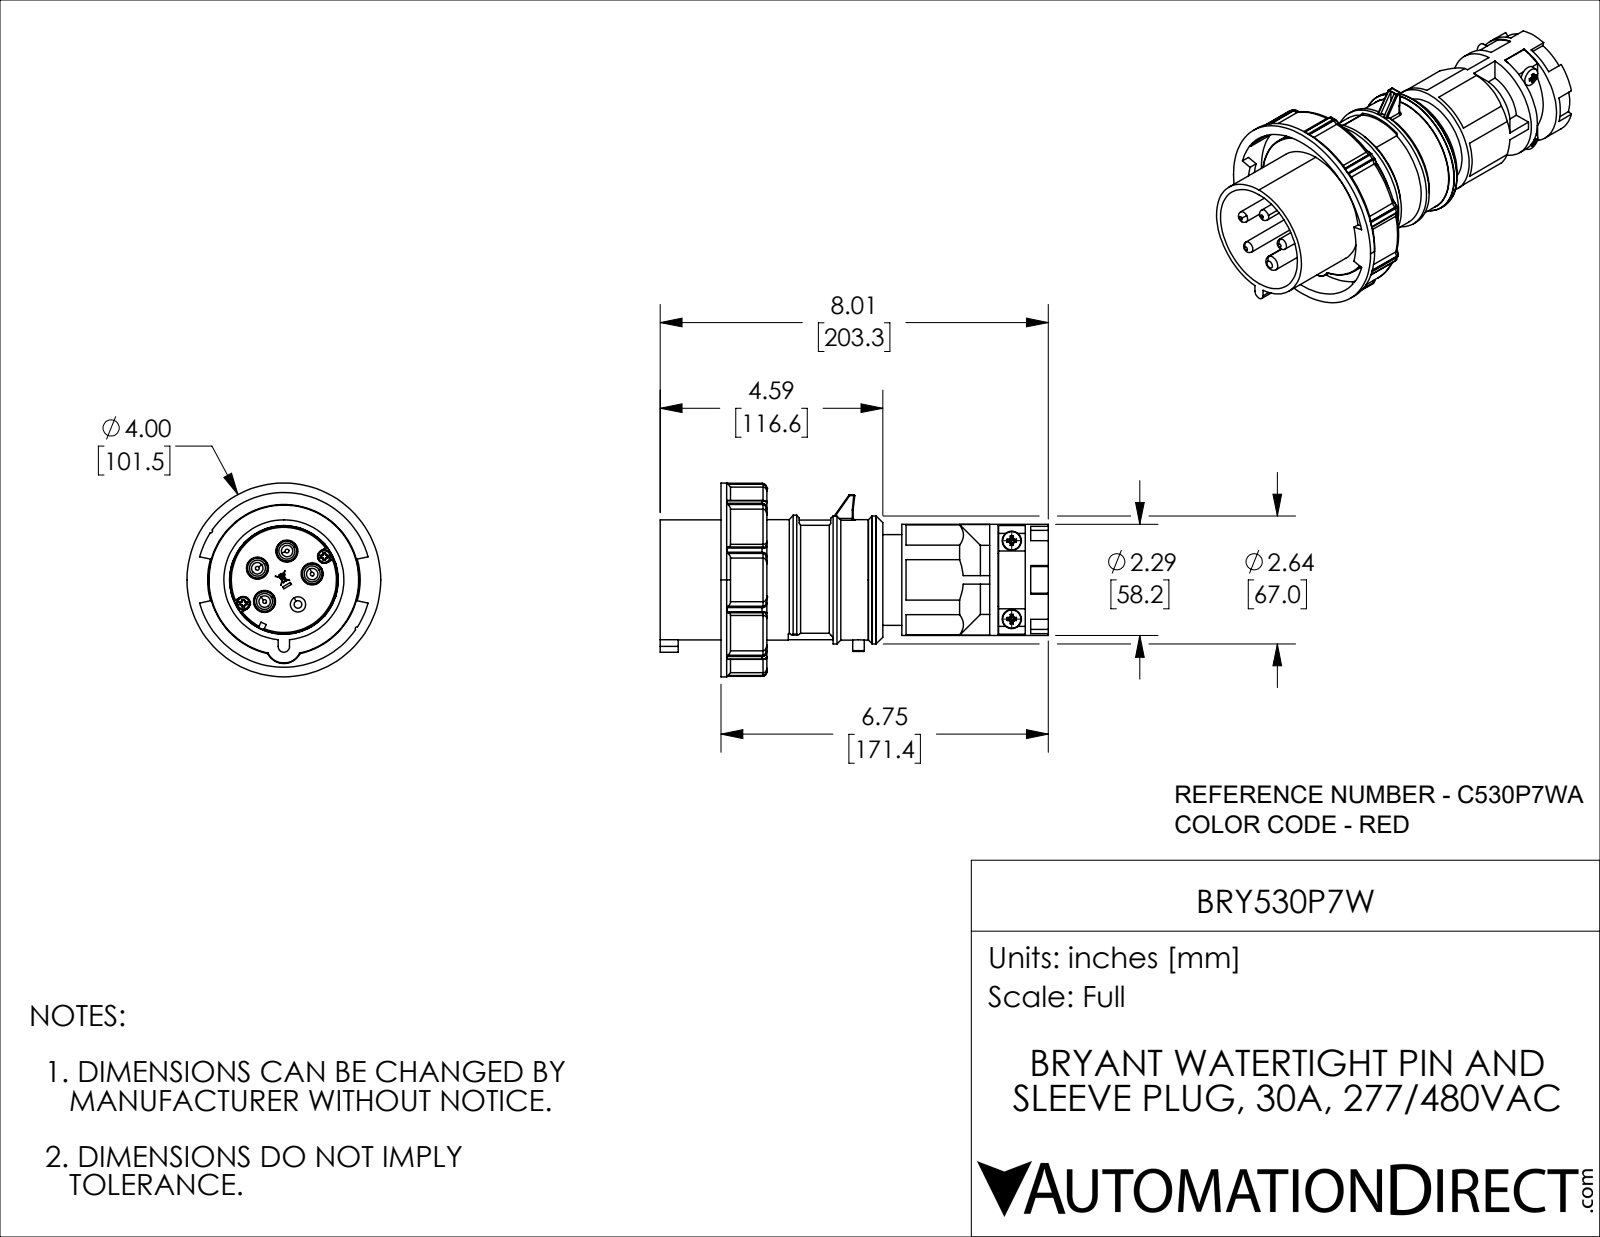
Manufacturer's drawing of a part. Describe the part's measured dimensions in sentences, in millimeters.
The part is named "BRY530P7W". Its 3-D file was written by "SolidWorks 2021 (CONFIG_CONTROL_DESIGN)". It is 6 solids with 861 faces: 337 planar, 266 cylindrical and 258 other. Overall it measures 203.33 by 101.5 by 101.5 millimeters. Its volume is 459 019 cubic millimeters and its surface area 104 002 square millimeters. Round holes: 2 of diameter 5, 1 of diameter 0.51, 1 of diameter 3.1, 1 of diameter 29.5, 1 of diameter 49.04, 1 of diameter 91.5. Round bosses or shafts: 5 of diameter 6, 1 of diameter 101.5, 1 of diameter 79, 1 of diameter 67.7, 1 of diameter 67, 1 of diameter 63, 1 of diameter 62.9, 1 of diameter 58.2. Partial cylindrical surfaces (rounded edges, fillets, slot ends): 30 of radius 0.5, 20 of radius 2.5, 12 of radius 1, 4 of radius 0.2, 4 of radius 0.75, 3 of radius 3, 2 of radius 0.3, 2 of radius 3.55. The main face-to-face distances are 70.73, 4.5, 64.7, 135.43, 10, 18.7, 60.73, 54.2, 3.5, 81.13. The hole center spacings are 1.18, 41.
